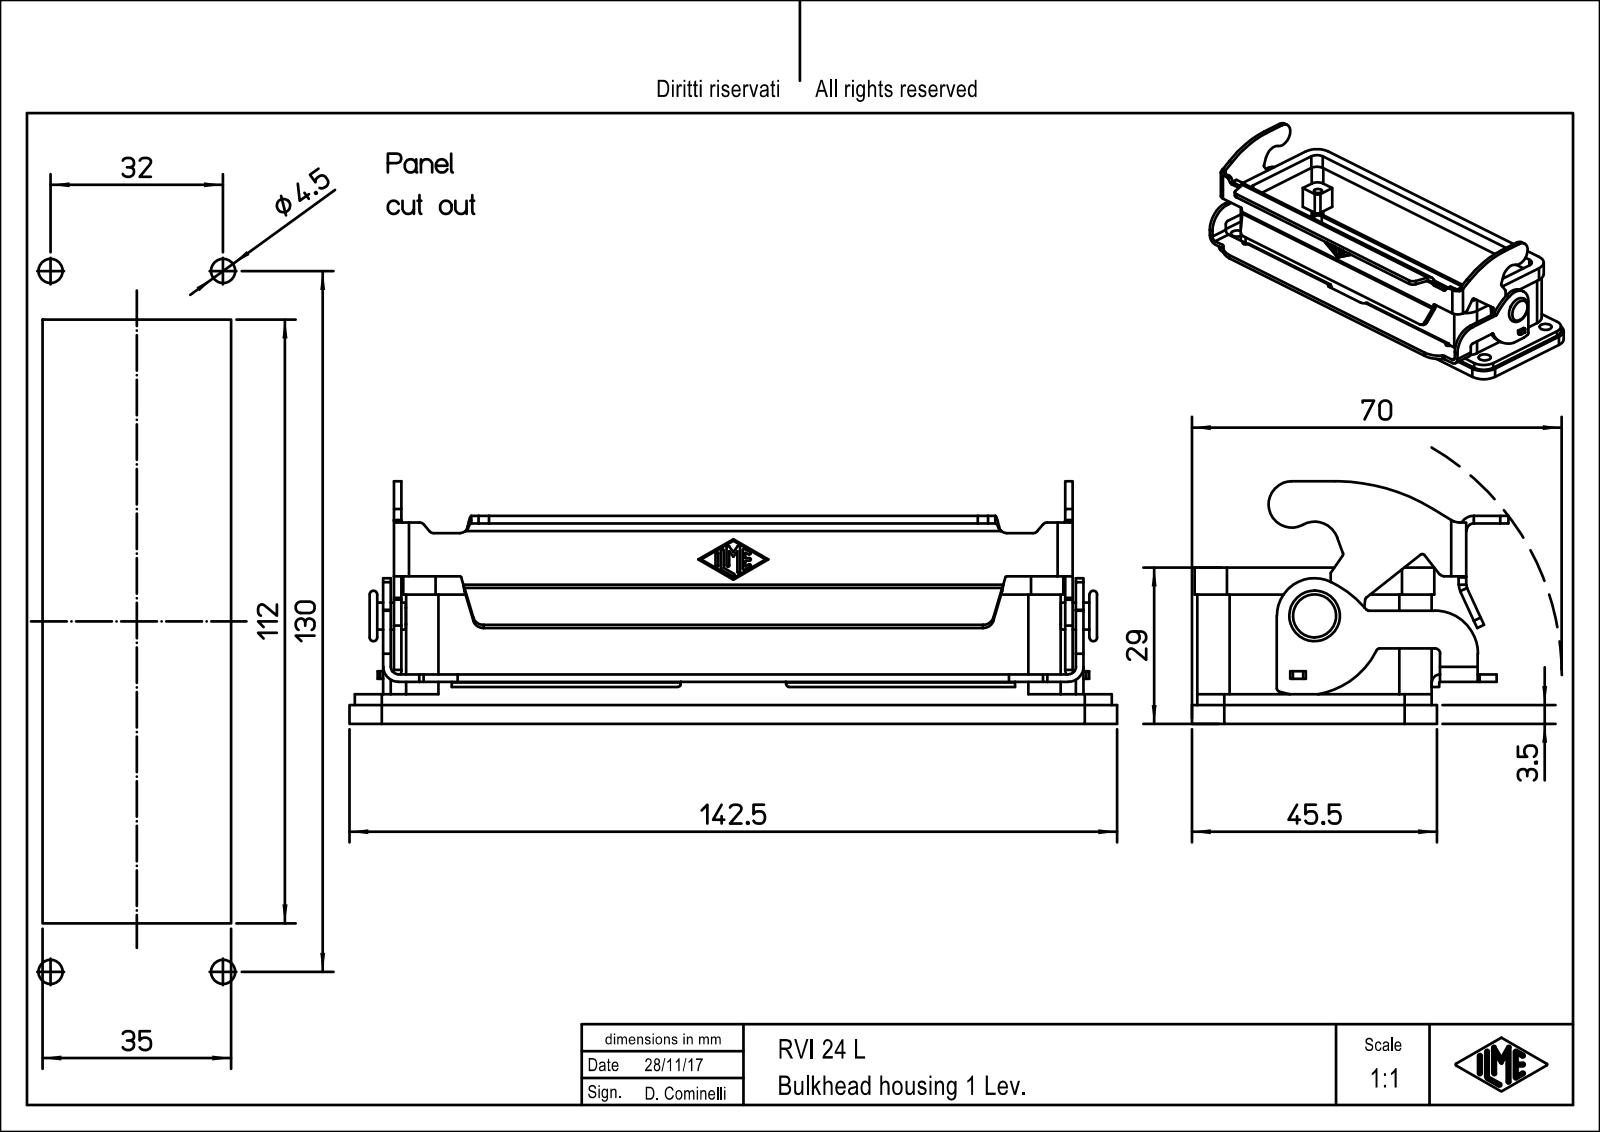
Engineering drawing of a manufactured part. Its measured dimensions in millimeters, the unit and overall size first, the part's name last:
Units: millimetres
Overall size (bounding box): 142.5 × 58.73 × 45
Round holes (diameter × count): ⌀2.46 ×4, ⌀3 ×4, ⌀4.5 ×4, ⌀4.5 ×4
Round bosses / shafts (diameter × count): ⌀5 ×1, ⌀3 ×1
Partial cylindrical surfaces — rounded edges, fillets, slot ends (radius × count): R0.25 ×16, R0.5 ×12, R1 ×12, R3 ×12, R6 ×12, R1.5 ×11, R2 ×8, R1.4 ×6
Main face-to-face distances: 40.5, 1.4, 3, 0.5, 3.5, 4, 2, 43.5, 37.5, 5.5
Hole centre spacings: 13.24, 32.24, 117.03, 120.66, 27, 32, 104, 107.45
Volume: 46 739 mm³ · Surface area: 39 703 mm²
Bodies: 1 solid, 403 faces (201 planar, 184 cylindrical, 18 other)
Part name (STEP PRODUCT): RVI_24_L
STEP written by: PTC Creo Elements/Direct Modeling 19.0E 27-Jun-2016 (C) Parametric Technology GmbH (AUTOMOTIVE_DESIGN)
